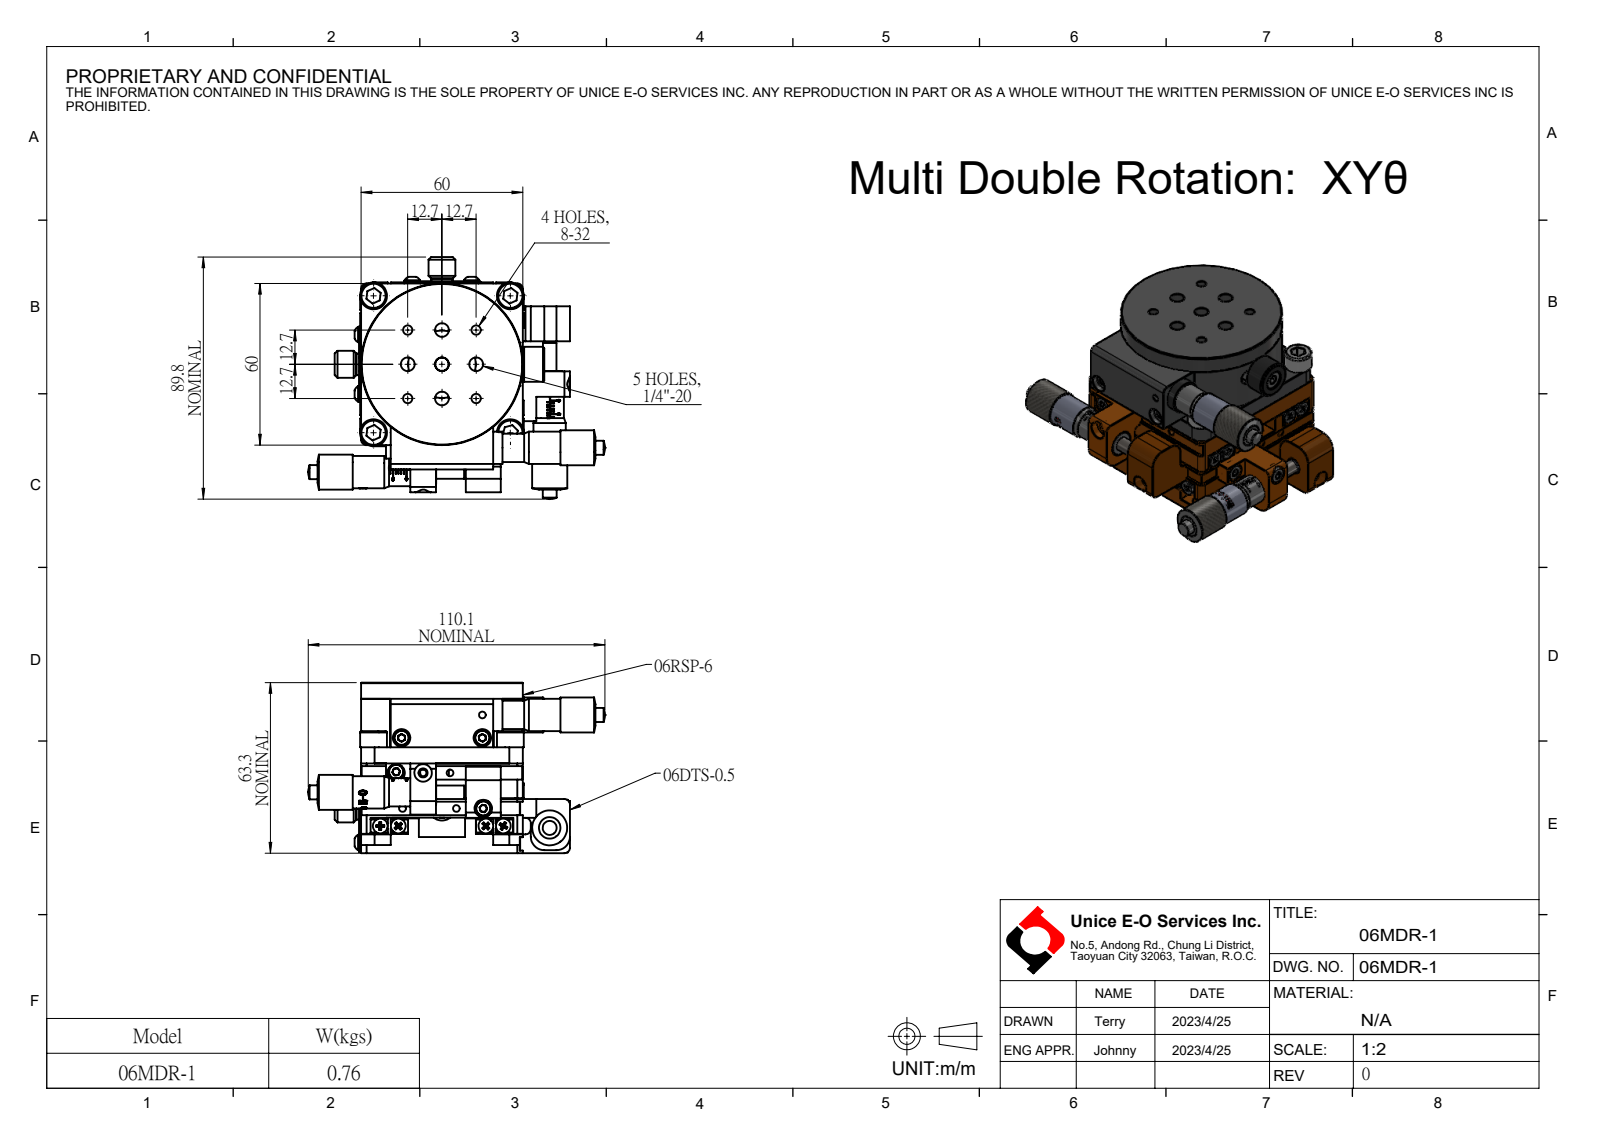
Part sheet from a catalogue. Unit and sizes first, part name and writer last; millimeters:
Units: millimetres
Overall size (bounding box): 110.15 × 89.8 × 63.3
Round holes (diameter × count): ⌀2.5 ×17, ⌀6.5 ×12, ⌀5.11 ×9, ⌀2.05 ×8, ⌀3.45 ×4, ⌀6 ×2, ⌀9.5 ×2, ⌀3.4 ×1, ⌀5 ×1, ⌀7.2 ×1, ⌀8.5 ×1, ⌀10.6 ×1
Round bosses / shafts (diameter × count): ⌀5.5 ×11, ⌀10 ×6, ⌀13 ×4, ⌀5.7 ×4, ⌀12 ×3, ⌀10.5 ×3, ⌀5.2 ×3, ⌀8 ×2
Partial cylindrical surfaces — rounded edges, fillets, slot ends (radius × count): R5 ×12, R2 ×11, R1.75 ×4, R6 ×4, R3 ×2, R5.98 ×2
Main face-to-face distances: 13.1, 6, 7, 13.2, 24, 57.3, 6.1, 13, 33.3, 20.1
Hole centre spacings: 28.4, 17.96, 25.4, 10, 12.7, 40.16, 35.92, 40
Bodies: 0 solids, 1156 faces (667 planar, 303 cylindrical, 186 other)
Part name (STEP PRODUCT): 06MDR-1
STEP written by: SolidWorks 2022 (CONFIG_CONTROL_DESIGN)
